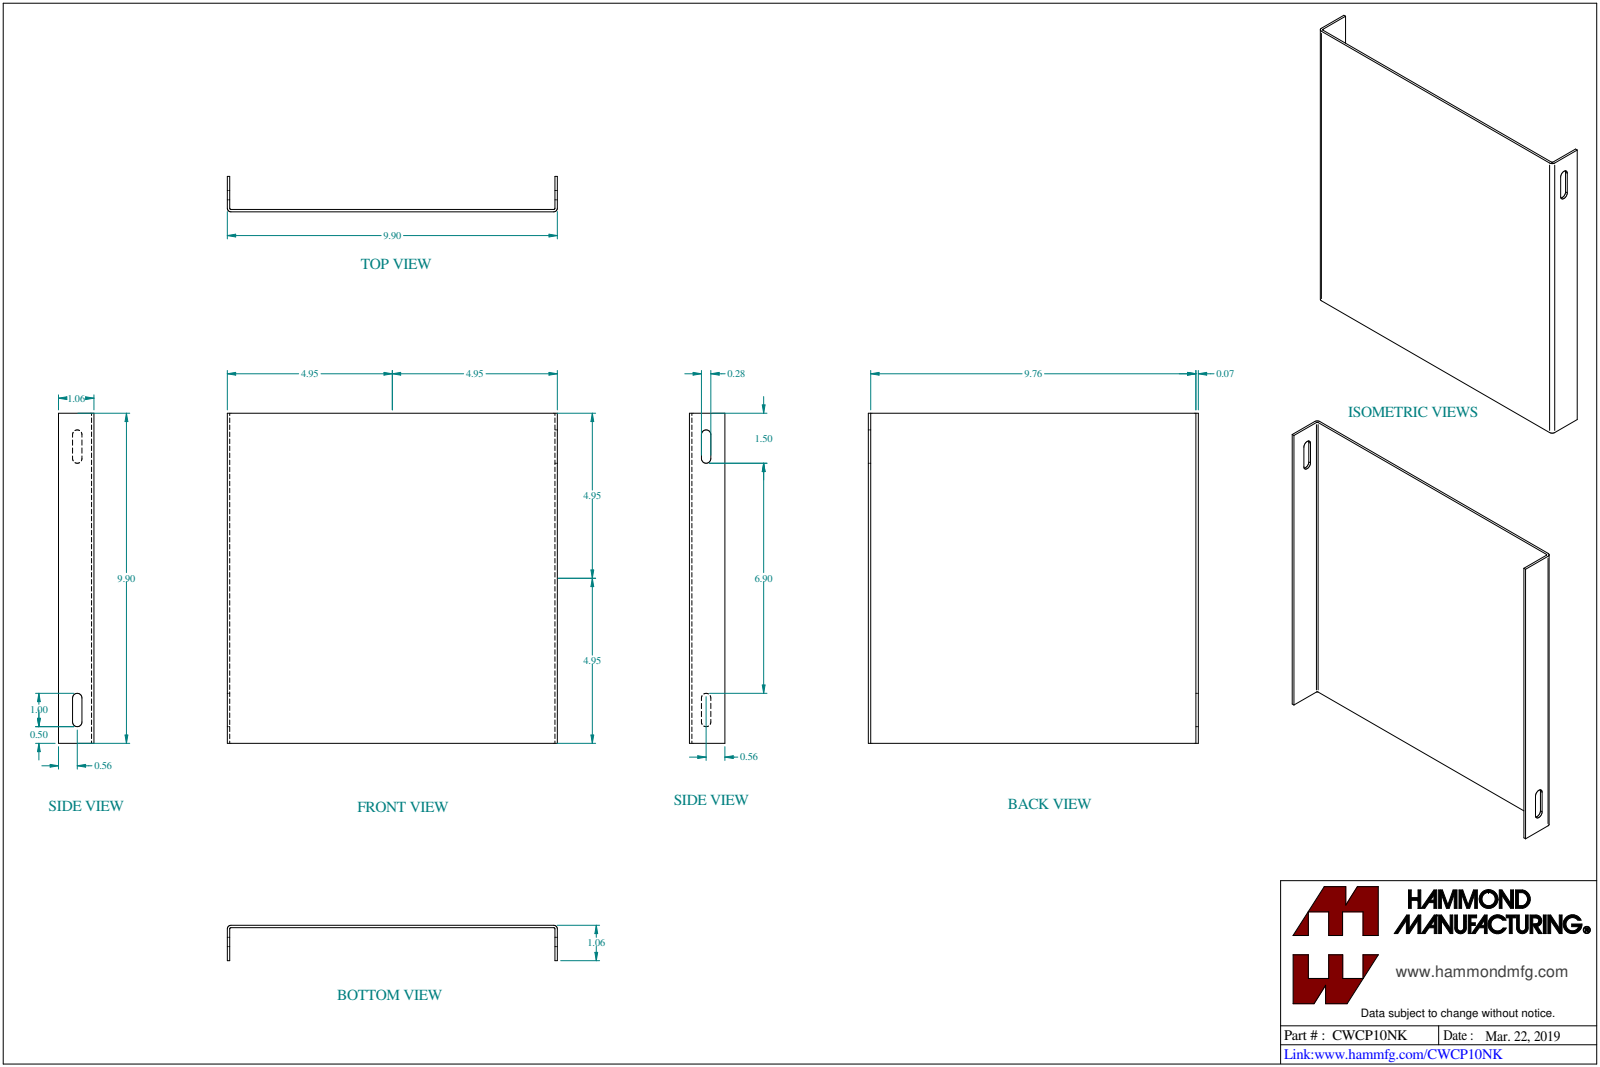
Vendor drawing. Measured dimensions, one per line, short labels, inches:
name: CWCP10NK
written by: SolidWorks 2023 (CONFIG_CONTROL_DESIGN)
unit: in
bodies: 1 solid, 22 faces (14 planar, 8 cylindrical, 0 other)
size: 9.9 × 9.9 × 1.062
volume: 8.387 in³; area: 236.4 in²
rounds: 4× R0.141, 2× R0.036, 2× R0.108
face distances: 0.072, 9.828, 9.9, 9.756, 1.063, 0.991, 0.359, 0.641, 0.287, 0.569
